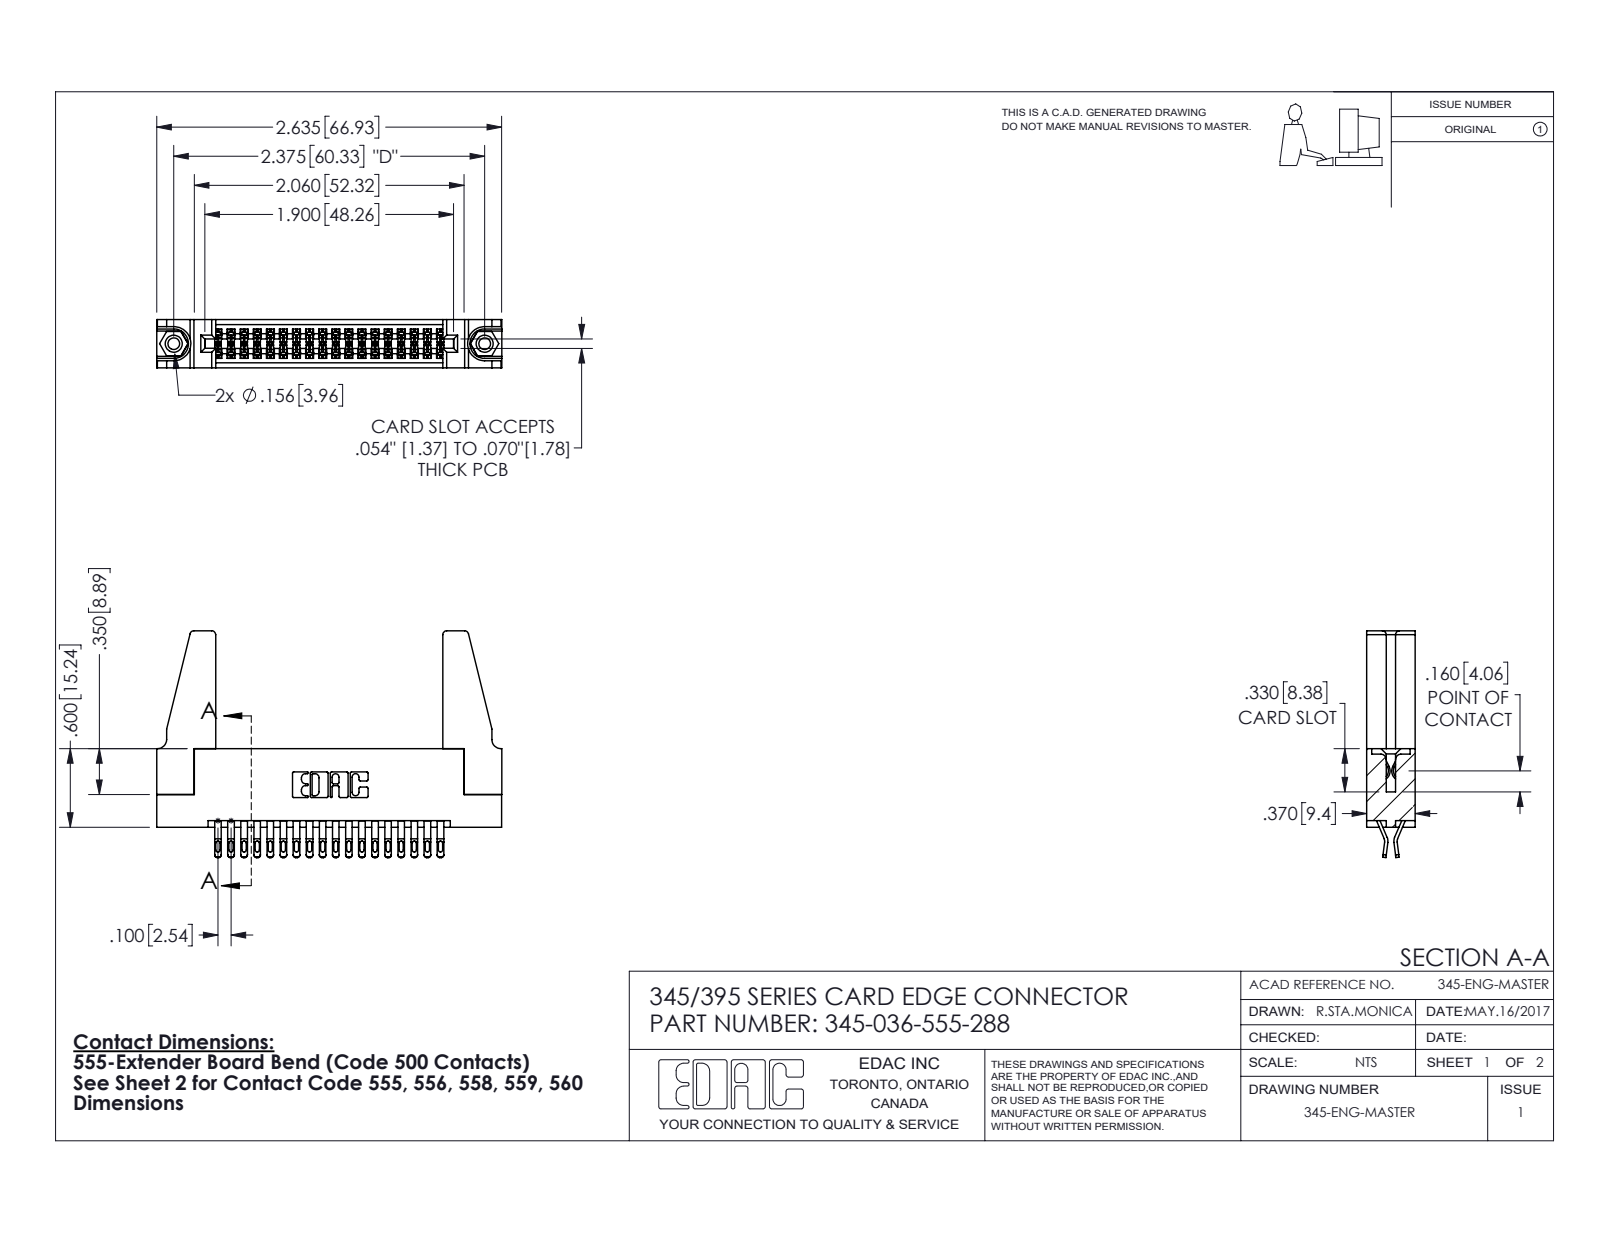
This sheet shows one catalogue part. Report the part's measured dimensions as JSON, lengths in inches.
{"part_name": "345-036-555-288; 345-292-001_555 Tail; 345 Part_Flush Mounting Lugs - 0.156 Dia-TH; 345-220-078_345-220-088 (+1 more)", "step_written_by": "SolidWorks 2016 (CONFIG_CONTROL_DESIGN)", "units": "inches", "bodies": {"solids": 41, "faces": 2266, "planar": 1268, "cylindrical": 982, "other": 16}, "overall_size": [2.636, 1.732, 0.37], "volume_in3": 0.588, "surface_area_in2": 19.31, "round_holes": [[0.089, 2], [0.125, 2], [0.156, 2], [0.064, 1]], "round_bosses_or_shafts": [[0.155, 2]], "partial_cylinders_radius": [[0.016, 90], [0.02, 72], [0.006, 54], [0.01, 22], [0.03, 8], [0.007, 6], [0.031, 6], [0.026, 3]], "face_to_face_distances": [0.37, 0.072, 0.298, 0.2, 0.025, 0.098, 0.272, 0.225, 0.175, 0.15], "hole_center_spacings": [0.27, 2.141, 2.375]}
